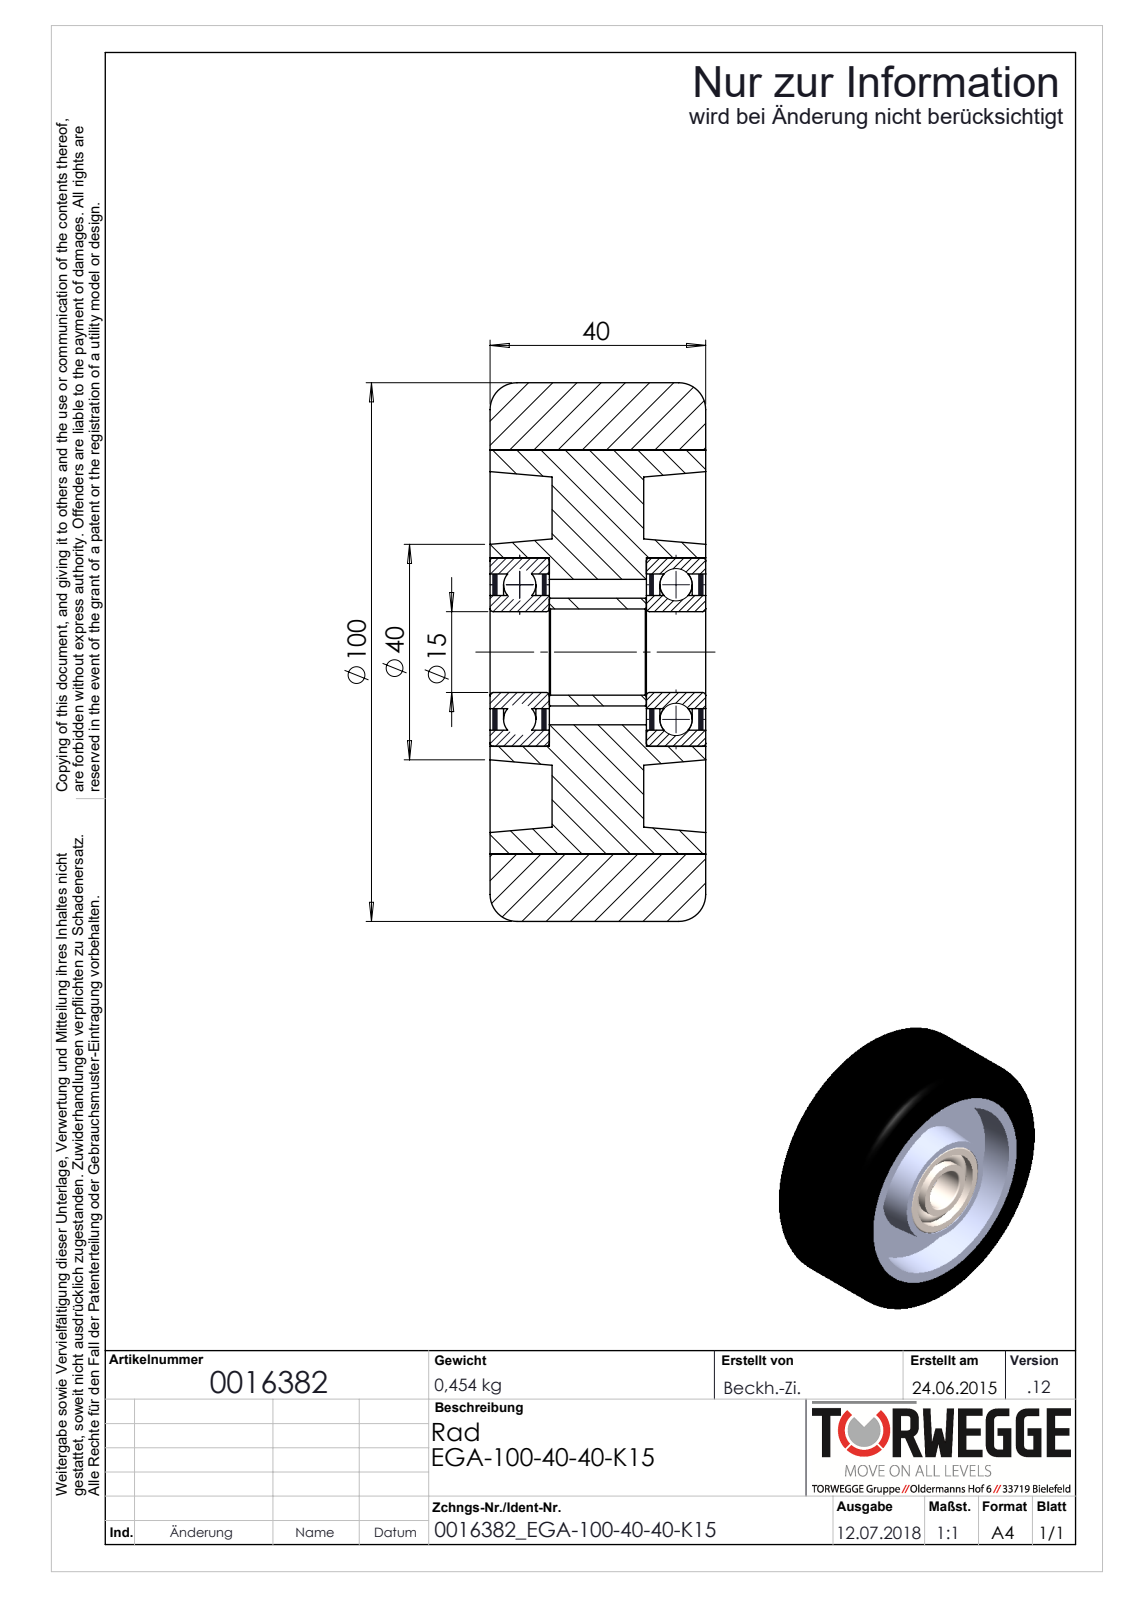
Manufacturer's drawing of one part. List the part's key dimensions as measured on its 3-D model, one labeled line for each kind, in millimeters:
Part name (STEP PRODUCT): 0016382_EGA-100-40-40-K15
STEP written by: SolidWorks 2014 (AUTOMOTIVE_DESIGN)
Units: millimetres
Bodies: 5 solids, 116 faces (24 planar, 48 cylindrical, 44 other)
Overall size (bounding box): 100 × 100 × 40
Volume: 247 540 mm³ · Surface area: 67 422 mm²
Round holes (diameter × count): ⌀15 ×1, ⌀16 ×1, ⌀27 ×1, ⌀29 ×1, ⌀35 ×1, ⌀75 ×1
Round bosses / shafts (diameter × count): ⌀100 ×1, ⌀21 ×1, ⌀20 ×1
Main face-to-face distances: 28.5, 11.5, 40, 0.5, 11, 17, 29, 17.5, 18, 1.5
